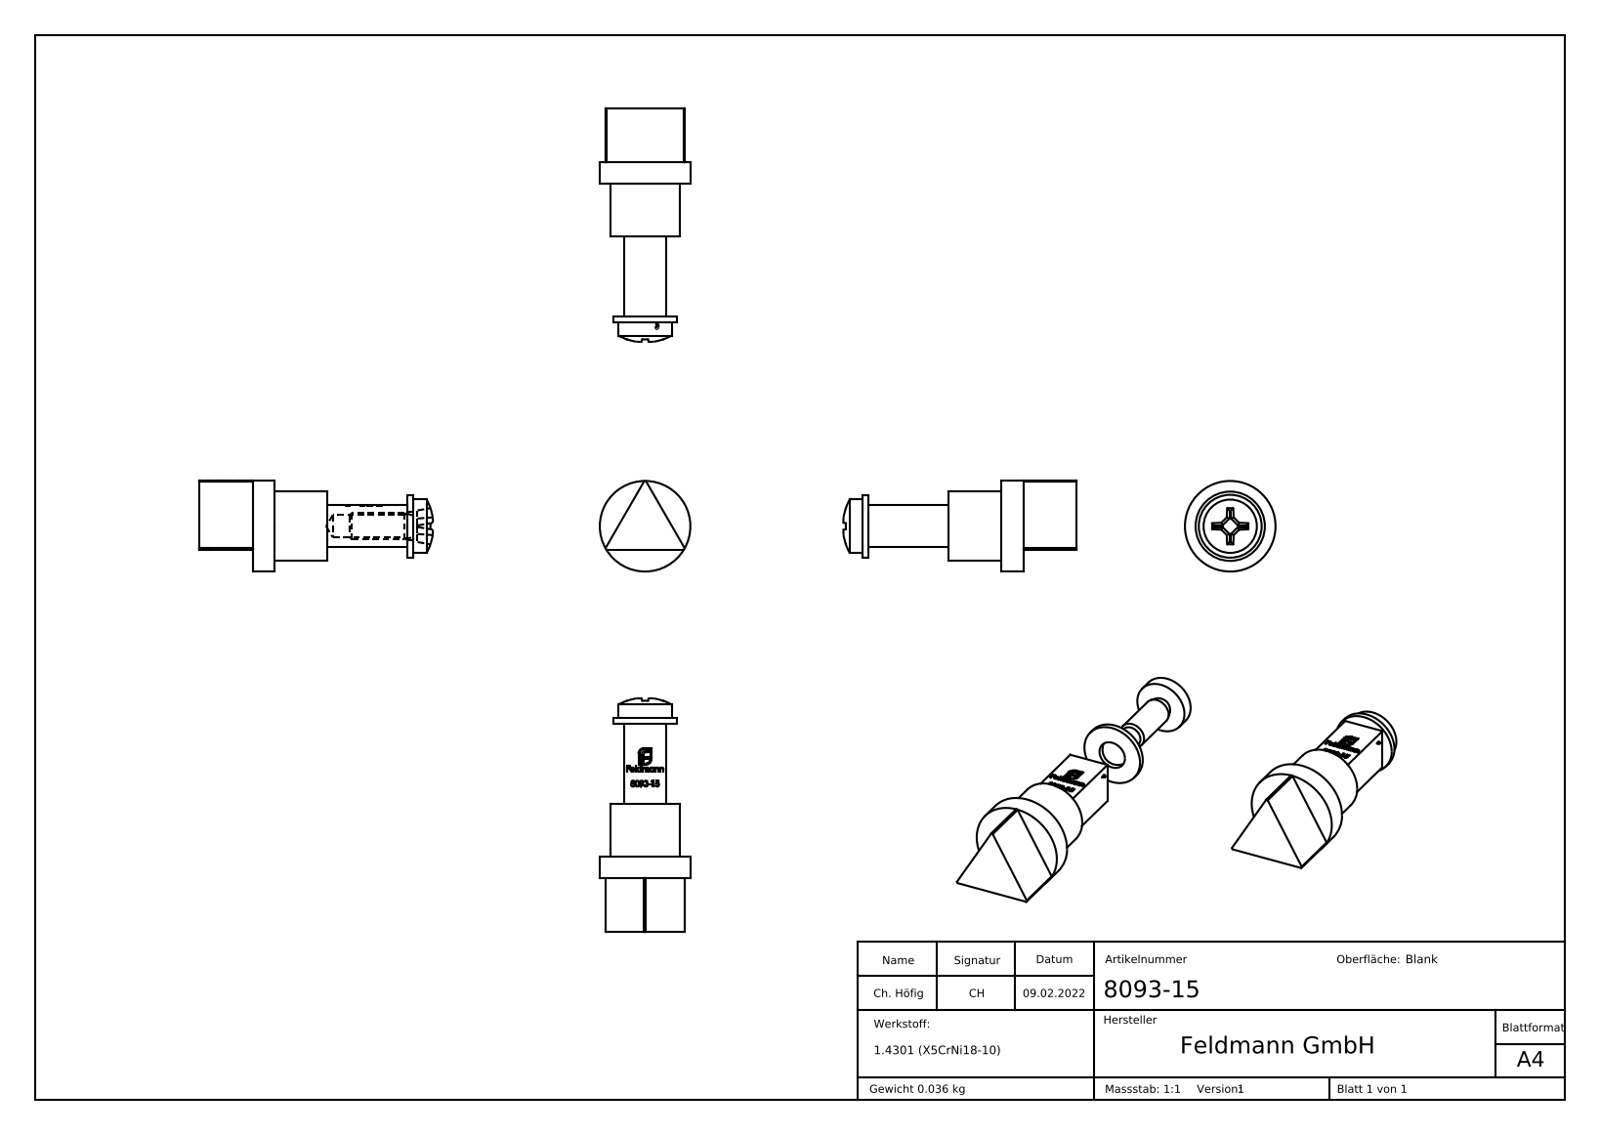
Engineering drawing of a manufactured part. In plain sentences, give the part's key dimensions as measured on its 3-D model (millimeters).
The part is named "8093-XX Teil2; 8093-XX Teil1; DIN 7045; 8093-XX Teil2_8093-XX Teil2 (+3 more)". Its 3-D file was written by "SolidWorks 2018 (CONFIG_CONTROL_DESIGN)". It is 3 solids with 312 faces: 156 planar, 21 cylindrical and 135 other. Overall it measures 43.77 by 17 by 17 millimeters. Its volume is 4 508 cubic millimeters and its surface area 2 902 square millimeters. Round holes: 1 of diameter 4.2, 1 of diameter 5.4. Round bosses or shafts: 1 of diameter 17, 1 of diameter 13, 1 of diameter 11.8, 1 of diameter 10, 1 of diameter 5. Partial cylindrical surfaces (rounded edges, fillets, slot ends): 6 of radius 0.1. The main face-to-face distances are 7.9, 30.1, 1.1, 29, 0.42, 8.32, 4.1, 40.1, 39, 10.
